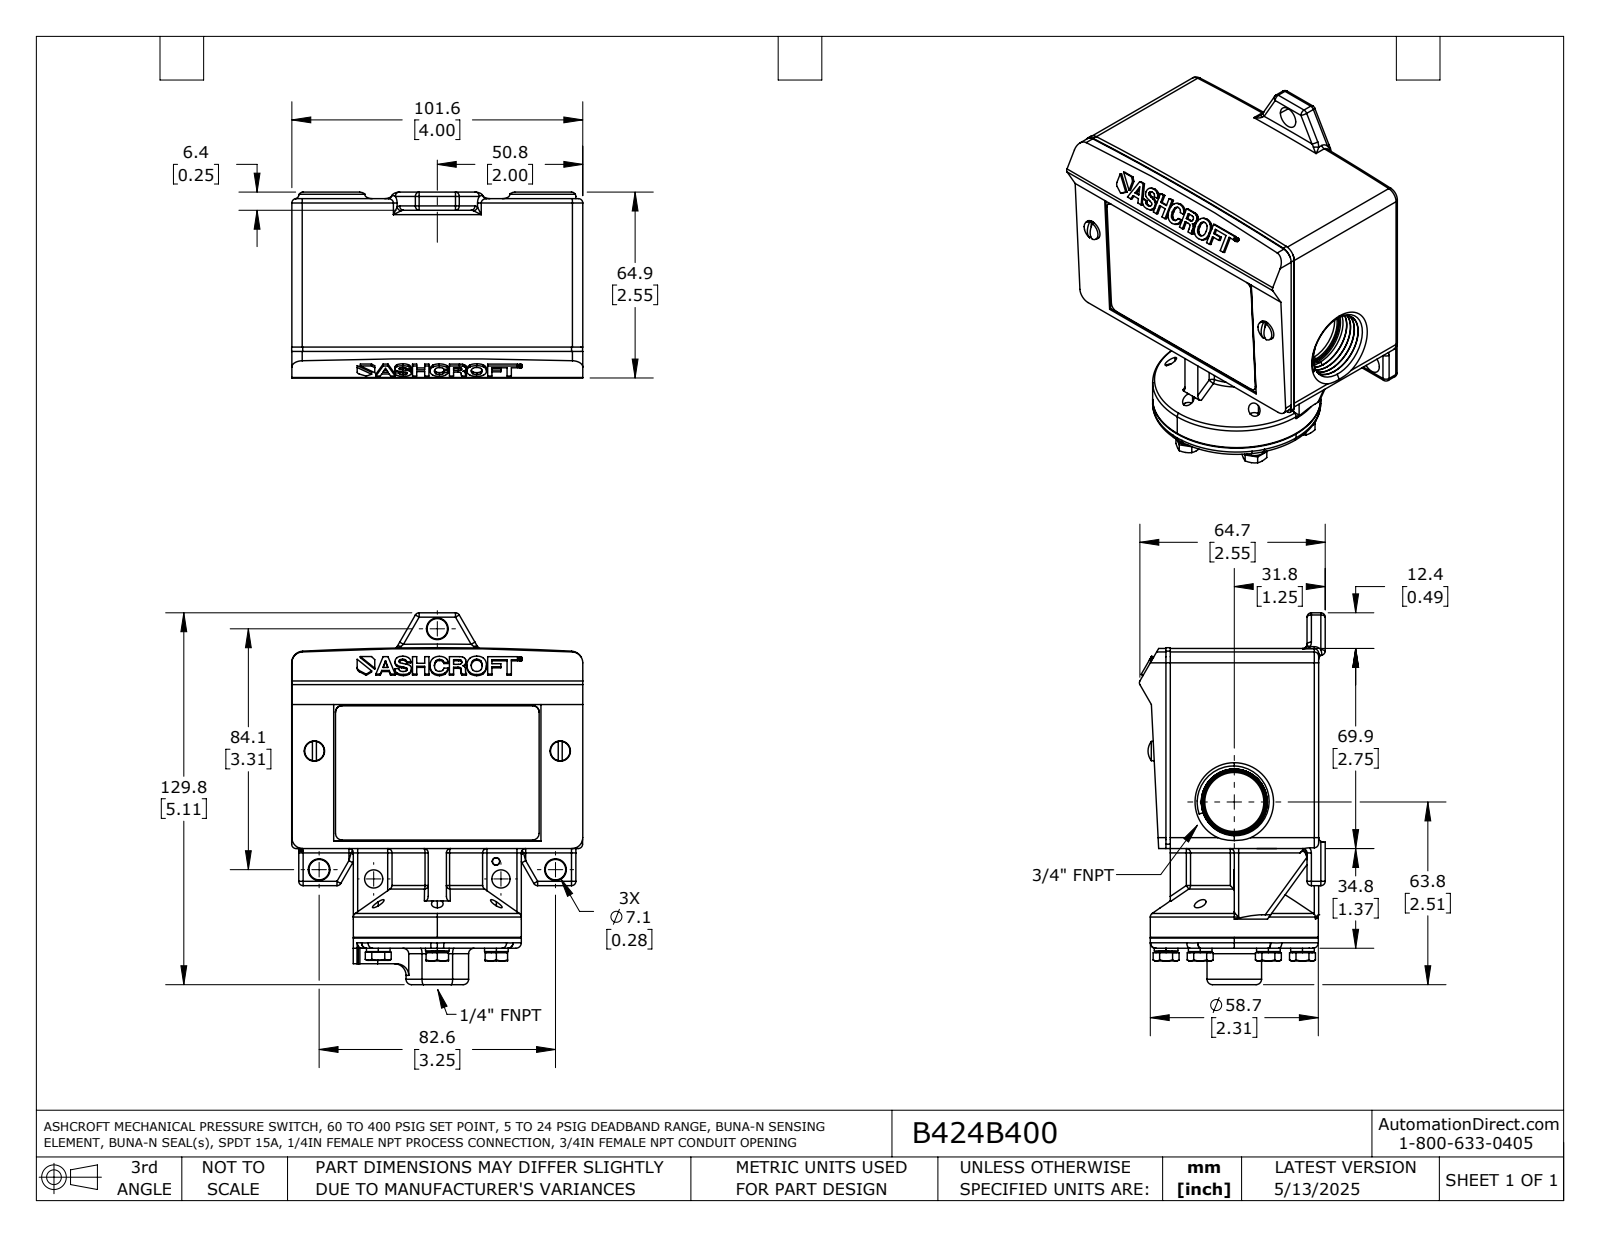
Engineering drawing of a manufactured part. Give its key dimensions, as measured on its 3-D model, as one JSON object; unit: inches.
{"part_name": "B424B400", "step_written_by": "SolidWorks 2021 (AUTOMOTIVE_DESIGN)", "units": "inches", "bodies": {"solids": 2, "faces": 1259, "planar": 345, "cylindrical": 472, "other": 442}, "overall_size": [5.111, 4.003, 2.555], "volume_in3": 28.57, "surface_area_in2": 84.51, "round_holes": [[0.161, 6], [0.192, 5], [0.209, 5], [0.187, 4], [0.28, 2], [0.455, 1], [0.812, 1]], "round_bosses_or_shafts": [[0.325, 6], [0.278, 6], [0.19, 5], [0.27, 2], [0.25, 2], [2.31, 1]], "partial_cylinders_radius": [[0.06, 92], [0.03, 5], [0.075, 4], [0.09, 4], [0.15, 4], [0.01, 2], [0.094, 2], [0.16, 2]], "face_to_face_distances": [4, 0.015, 1.37, 0.09, 3.91, 0.44, 3.56, 3.47, 0.35, 0.845], "hole_center_spacings": [0.937, 1.624, 1.875, 0.938, 3.38]}
